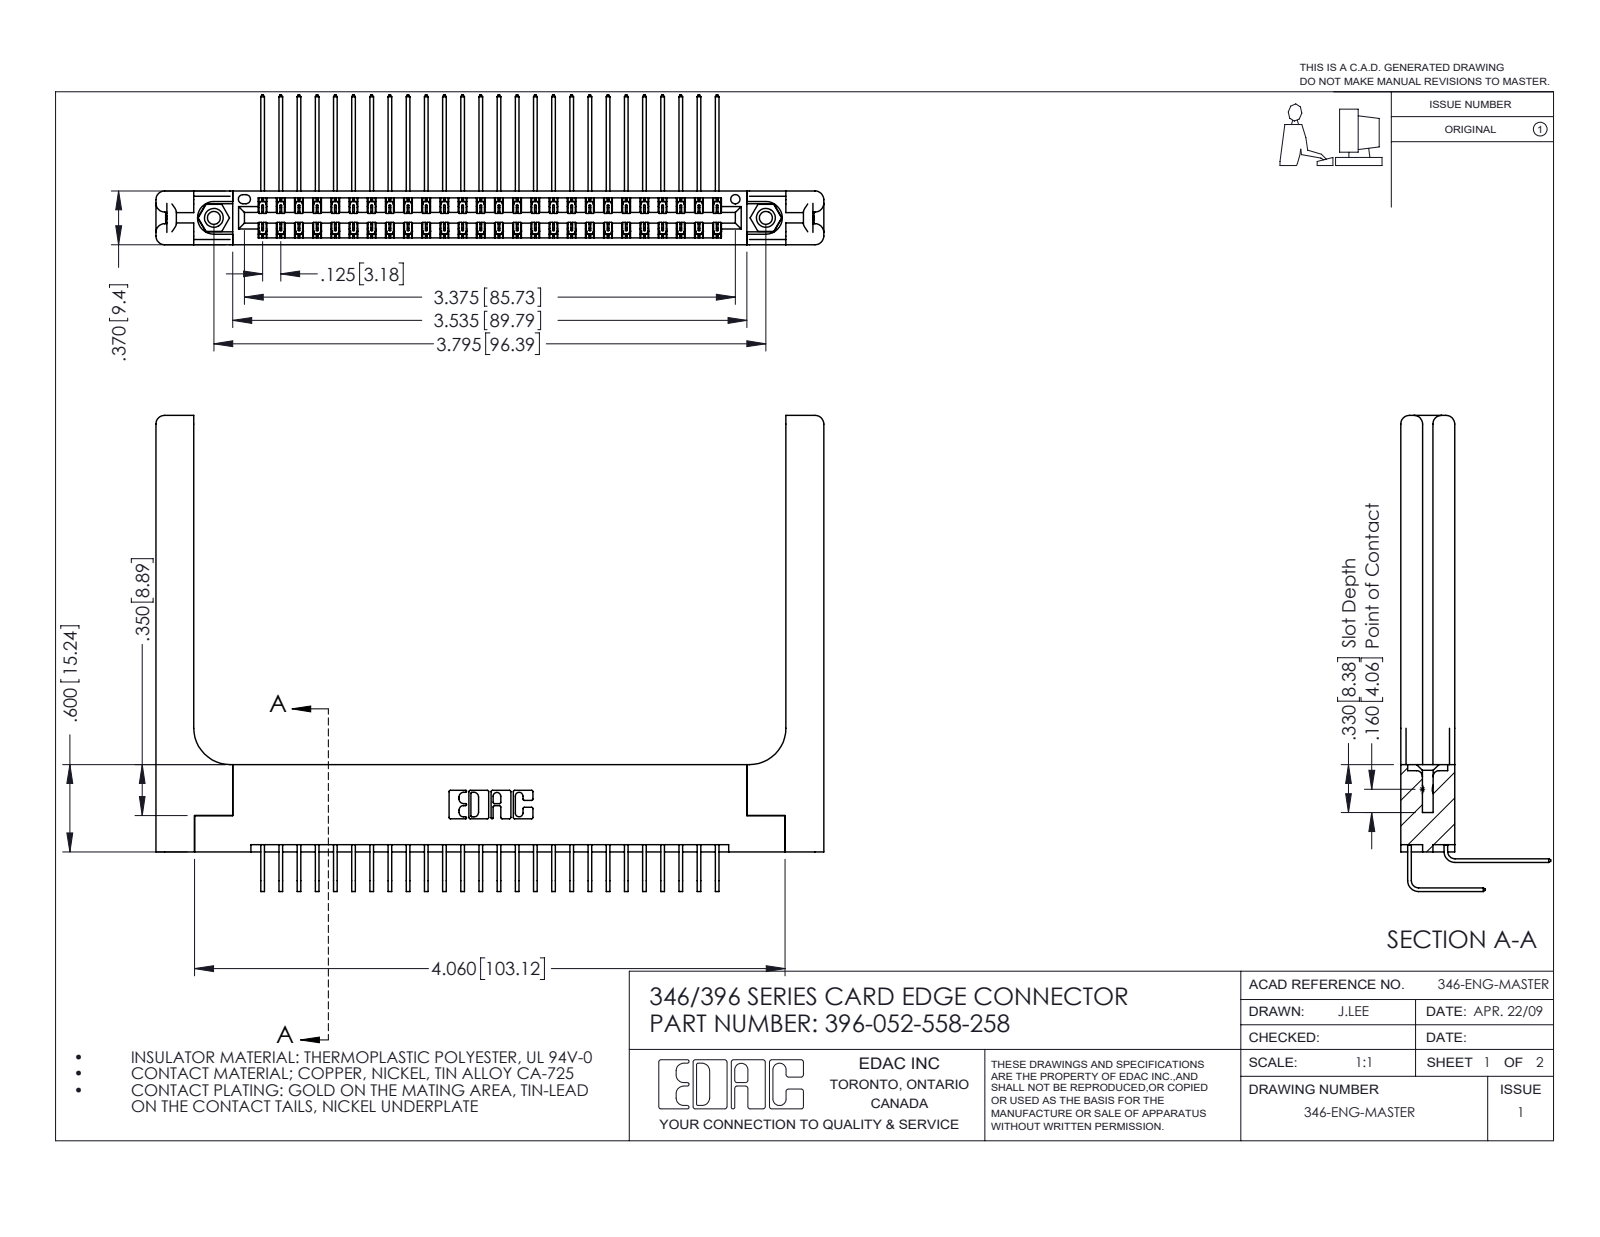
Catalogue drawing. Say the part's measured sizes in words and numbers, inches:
The part is named "346 Part_Flush Mounting Lugs - 0.156 Dia-TH; 345-292-001_558 559 Tail - 1; 396-052-558-258; 346-220-058_345-220-058 (+2 more)". Its 3-D file was written by "SolidWorks 2016 (CONFIG_CONTROL_DESIGN)". It is 57 solids with 3186 faces: 2148 planar, 978 cylindrical and 60 other. Overall it measures 4.591 by 3.273 by 1.03 inches. Its volume is 1.162 cubic inches and its surface area 34.15 square inches. Round holes: 2 of diameter 0.089, 2 of diameter 0.125, 2 of diameter 0.156, 1 of diameter 0.064. Round bosses or shafts: 2 of diameter 0.155. Partial cylindrical surfaces (rounded edges, fillets, slot ends): 78 of radius 0.006, 22 of radius 0.01, 16 of radius 0.06, 6 of radius 0.007, 6 of radius 0.031, 3 of radius 0.026, 2 of radius 0.014, 2 of radius 0.022. The main face-to-face distances are 0.37, 0.322, 0.072, 0.048, 0.025, 0.148, 0.15, 0.298, 0.25, 0.275. The hole center spacings are 0.246, 3.587, 3.795.
